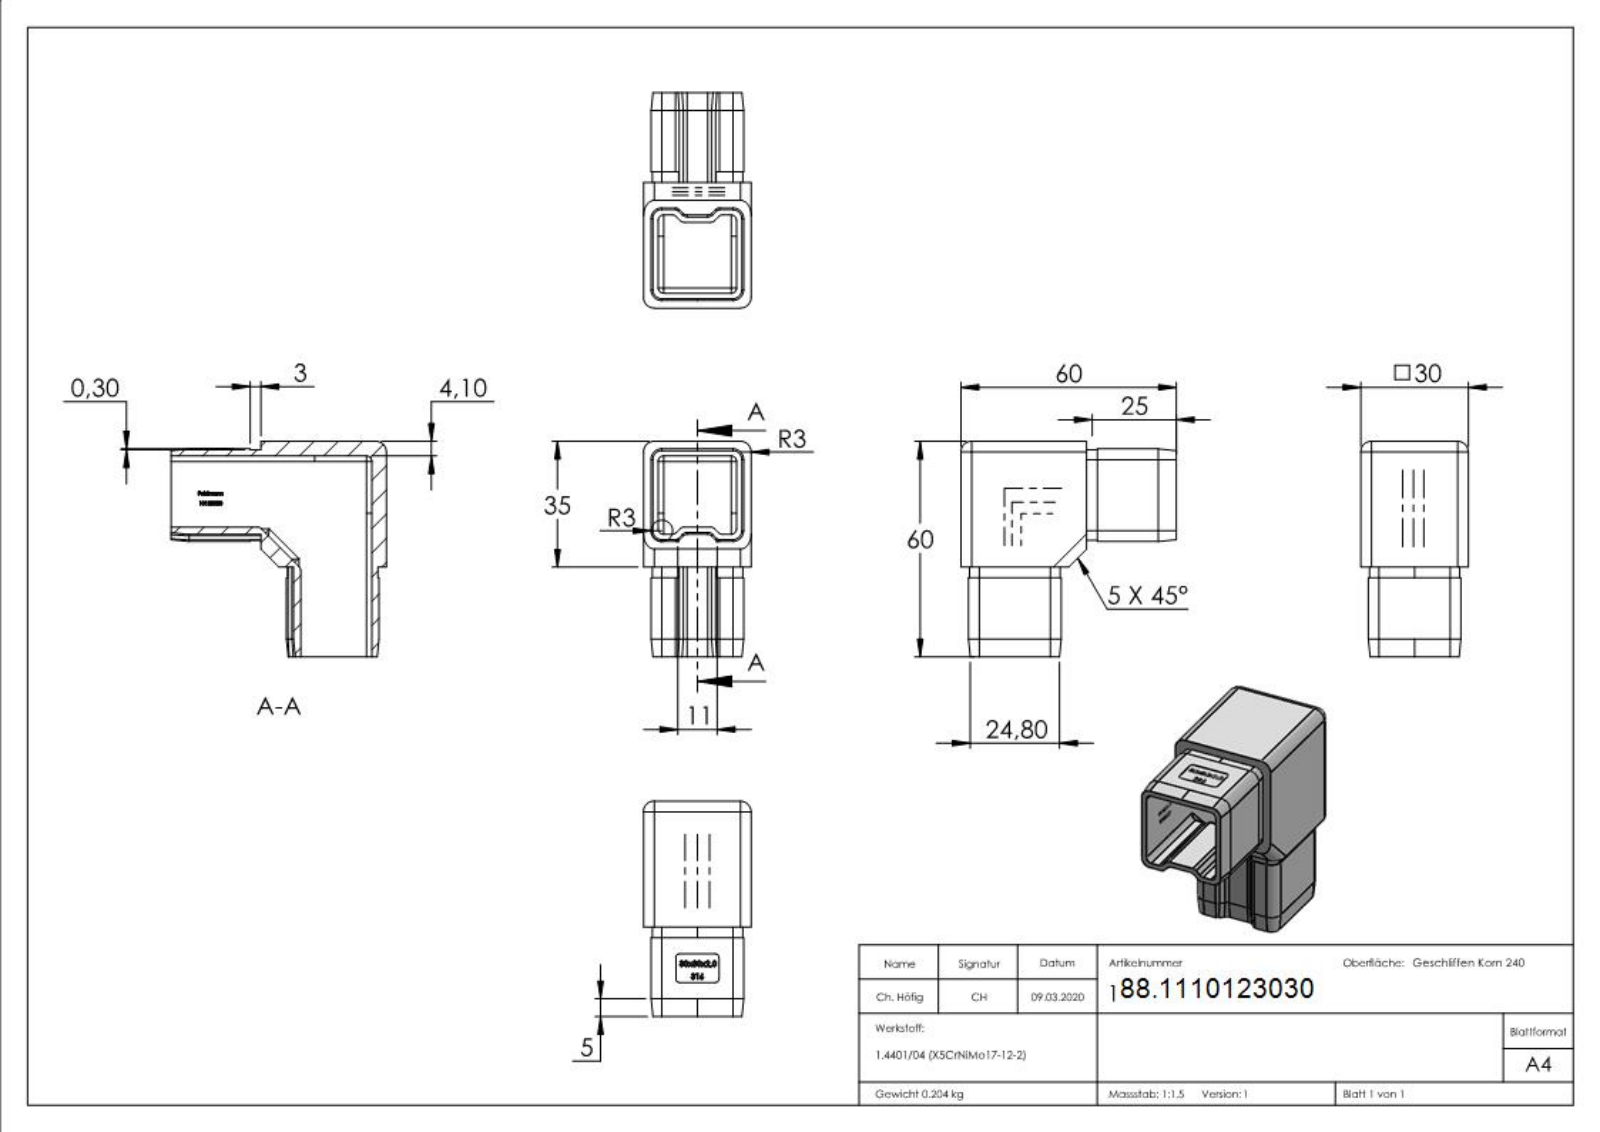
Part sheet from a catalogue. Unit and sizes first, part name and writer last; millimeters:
Units: millimetres
Overall size (bounding box): 60 × 60 × 30
Partial cylindrical surfaces — rounded edges, fillets, slot ends (radius × count): R1.5 ×35, R3 ×15, R2.7 ×8, R1 ×4
Main face-to-face distances: 4.1, 2, 21.8, 25.9, 23.8, 2.1, 27.9, 30, 25.8, 30.9
Volume: 25 513 mm³ · Surface area: 18 004 mm²
Bodies: 1 solid, 556 faces (264 planar, 68 cylindrical, 224 other)
Part name (STEP PRODUCT): 10123030
STEP written by: SolidWorks 2015 (CONFIG_CONTROL_DESIGN)
